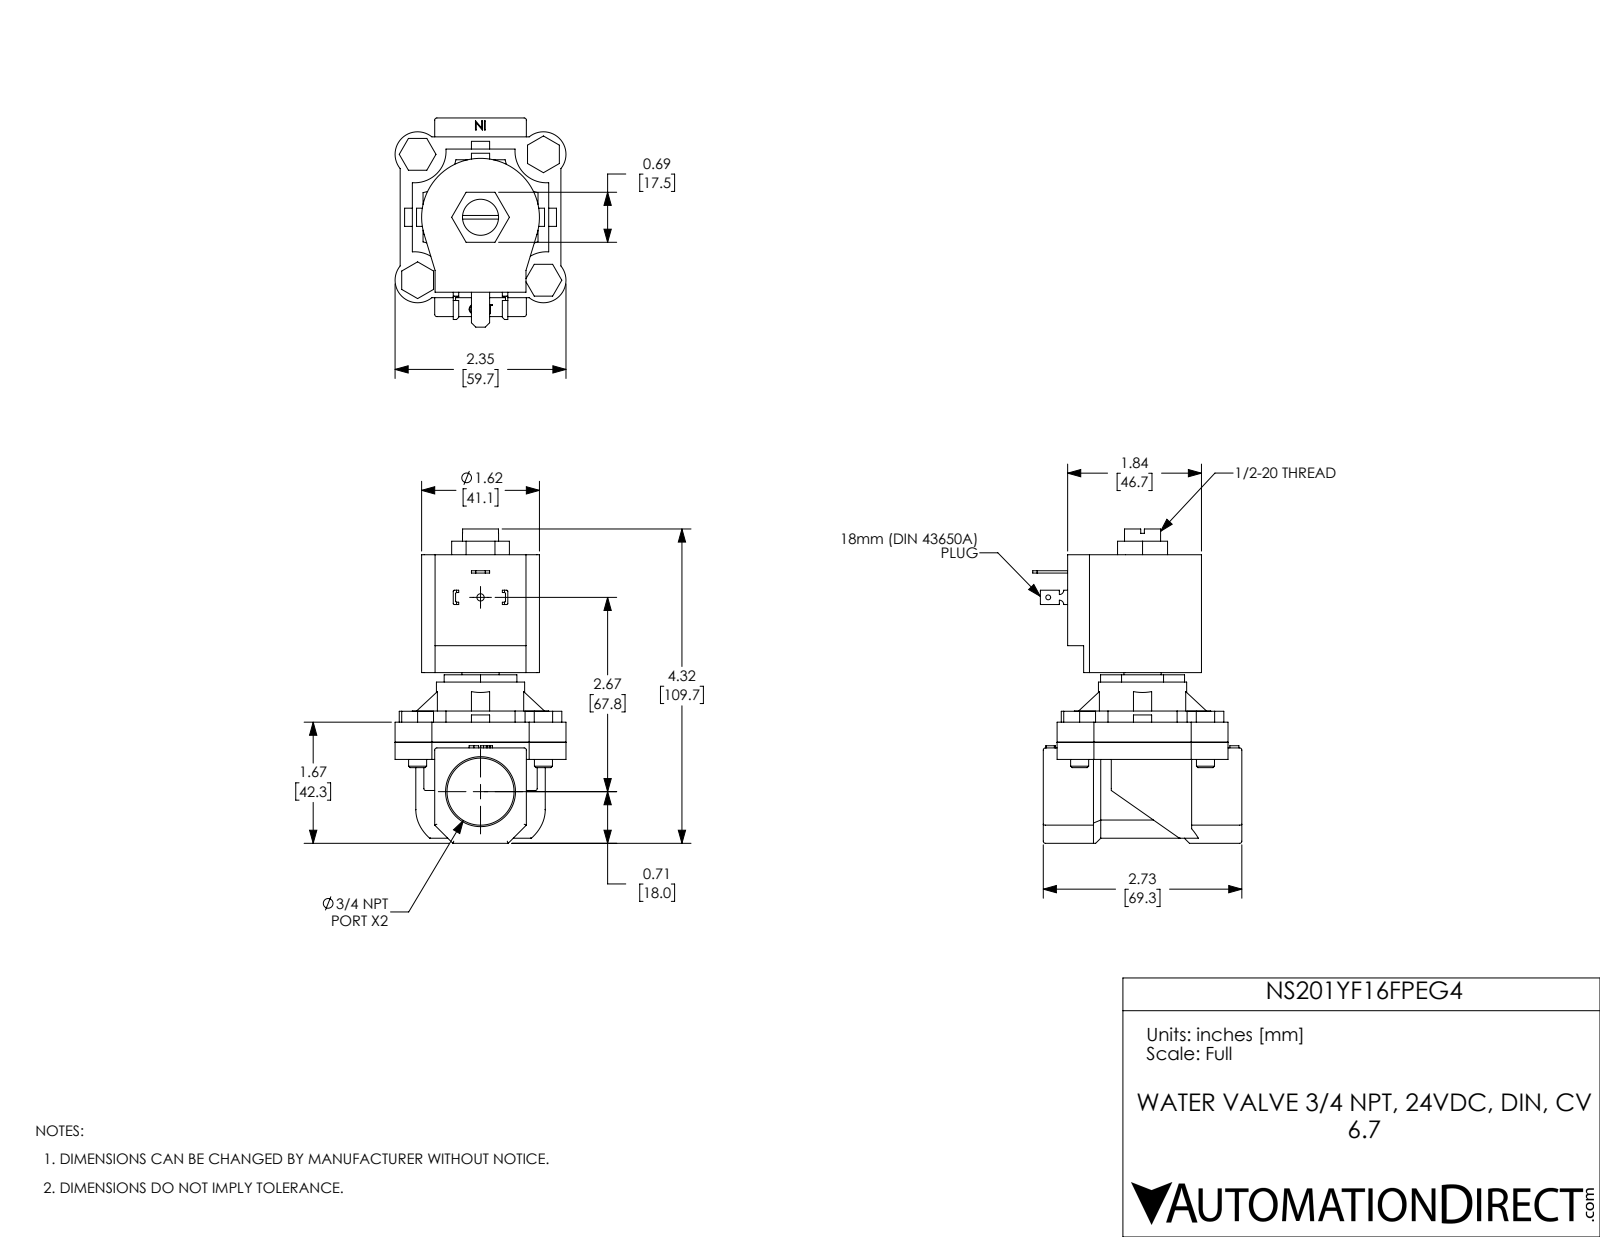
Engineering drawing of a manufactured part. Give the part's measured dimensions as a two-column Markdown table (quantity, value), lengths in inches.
| quantity | value |
| --- | --- |
| part name | NS201YF16FPEG5 |
| STEP written by | SolidWorks 2017 (AUTOMOTIVE_DESIGN) |
| units | inches |
| bodies | 11 solids, 387 faces (241 planar, 113 cylindrical, 33 other) |
| overall size | 4.32 × 2.875 × 2.35 |
| volume | 10.62 in³ |
| surface area | 70.92 in² |
| round holes (diameter × count) | 0.25 × 4, 0.067 × 1, 0.1 × 1, 0.496 × 1, 0.512 × 1, 0.922 × 1, 1.155 × 1 |
| round bosses / shafts (diameter × count) | 0.248 × 4, 1.213 × 1 |
| partial cylindrical surfaces (radius × count) | 0.03 × 15, 0.015 × 8, 0.31 × 4, 0.432 × 4, 0.579 × 4, 0.06 × 2, 0.81 × 1, 0.89 × 1 |
| main face-to-face distances | 0.276, 2.577, 2.301, 0.236, 0.512, 2.813, 0.475, 1.735, 1.26, 2.21 |
| hole center spacings | 1.223, 1.73, 2.446, 2.67 |
